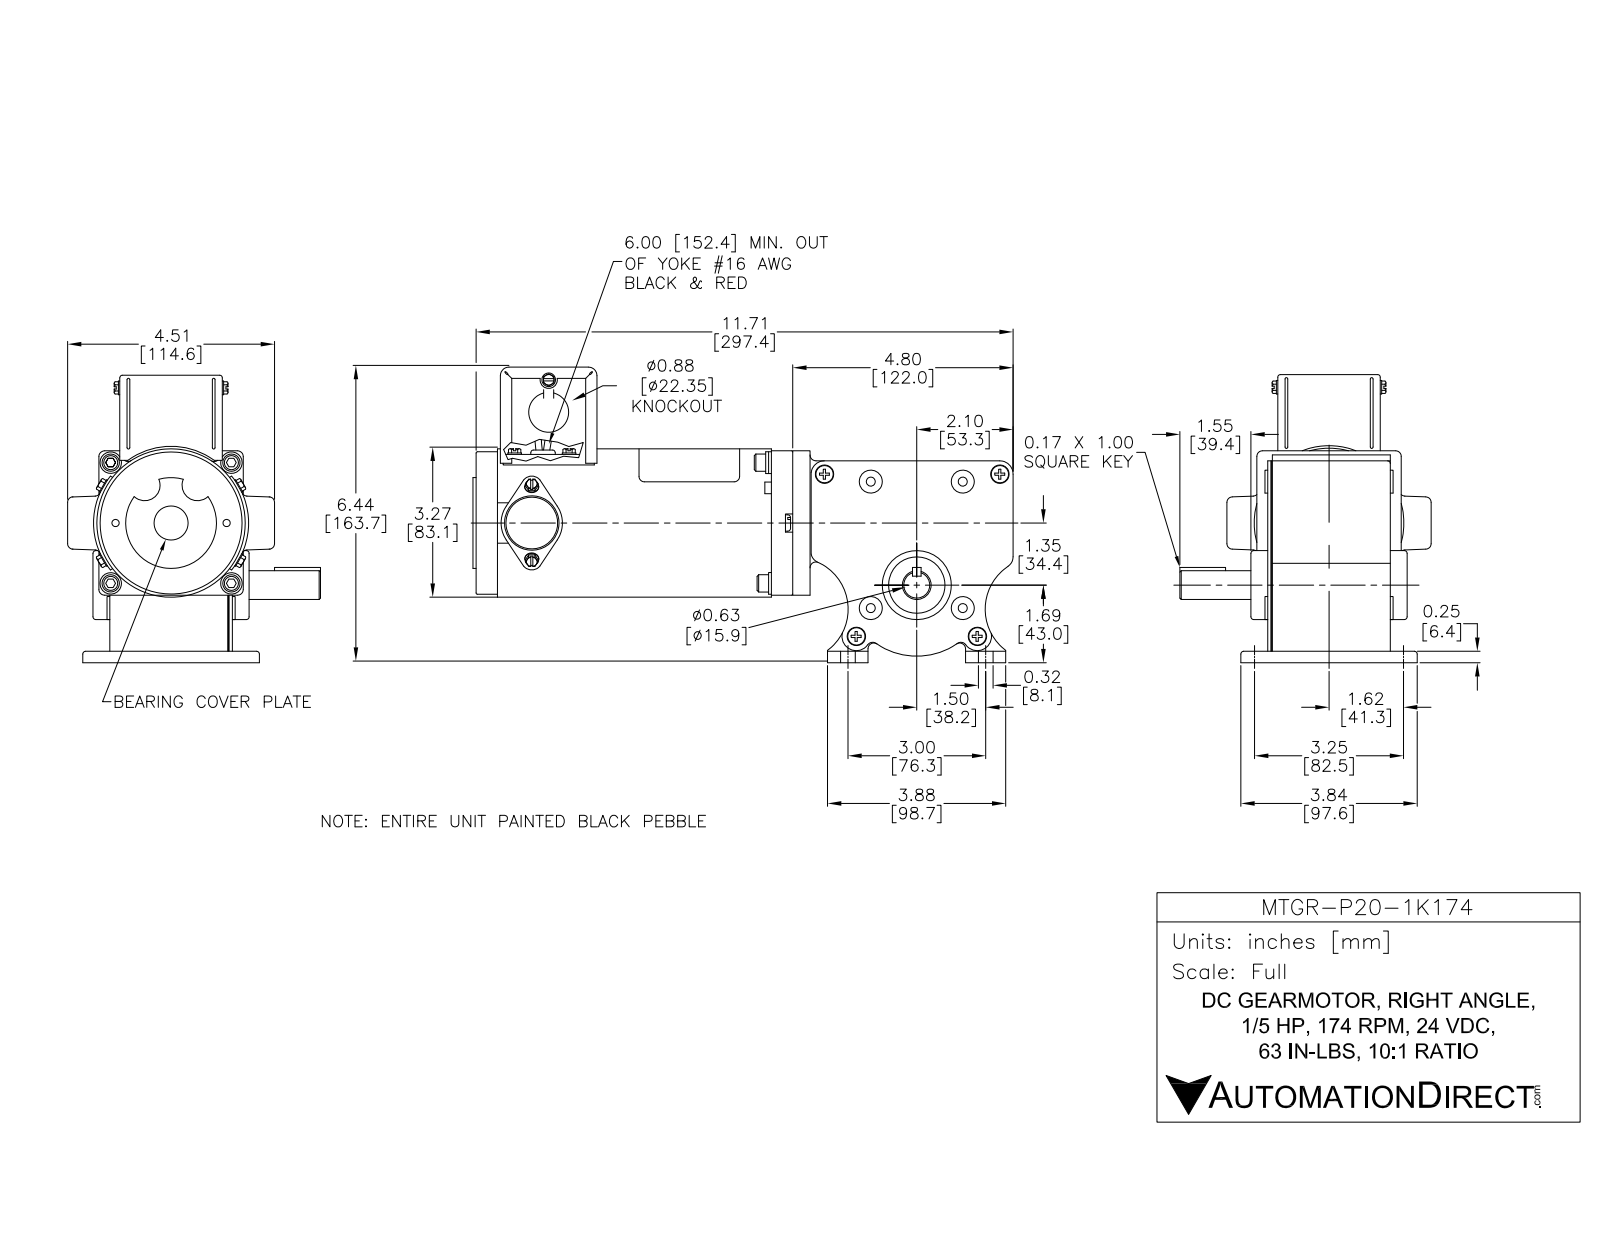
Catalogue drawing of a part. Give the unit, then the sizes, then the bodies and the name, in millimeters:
Units: millimetres
Overall size (bounding box): 299.5 × 165.7 × 137.5
Round holes (diameter × count): ⌀12.7 ×5, ⌀3.2 ×4, ⌀5 ×4, ⌀10.2 ×4, ⌀5 ×2, ⌀6.4 ×1, ⌀7.6 ×1, ⌀9.5 ×1, ⌀15.9 ×1, ⌀25.4 ×1, ⌀28.6 ×1, ⌀38.1 ×1
Round bosses / shafts (diameter × count): ⌀9.5 ×6, ⌀7.6 ×4, ⌀9.5 ×3, ⌀3.2 ×2, ⌀2.5 ×2, ⌀80.2 ×1, ⌀15.9 ×1, ⌀7.6 ×1
Partial cylindrical surfaces — rounded edges, fillets, slot ends (radius × count): R3.2 ×4, R4.1 ×4, R4.9 ×4, R5.9 ×4, R6.4 ×4, R3.3 ×2, R4 ×2, R7.4 ×2
Main face-to-face distances: 0.4, 0.8, 0.8, 66.1, 65.7, 65.4, 2.5, 1.8, 2.2, 67.9
Hole centre spacings: 33.5, 47.2, 66.8, 72.8, 28.4, 31.2, 50.8, 60.2
Volume: 1 059 000 mm³ · Surface area: 306 900 mm²
Bodies: 43 solids, 797 faces (486 planar, 283 cylindrical, 28 other)
Part name (STEP PRODUCT): P20-1K077
STEP written by: SolidWorks 2013 (AUTOMOTIVE_DESIGN)
